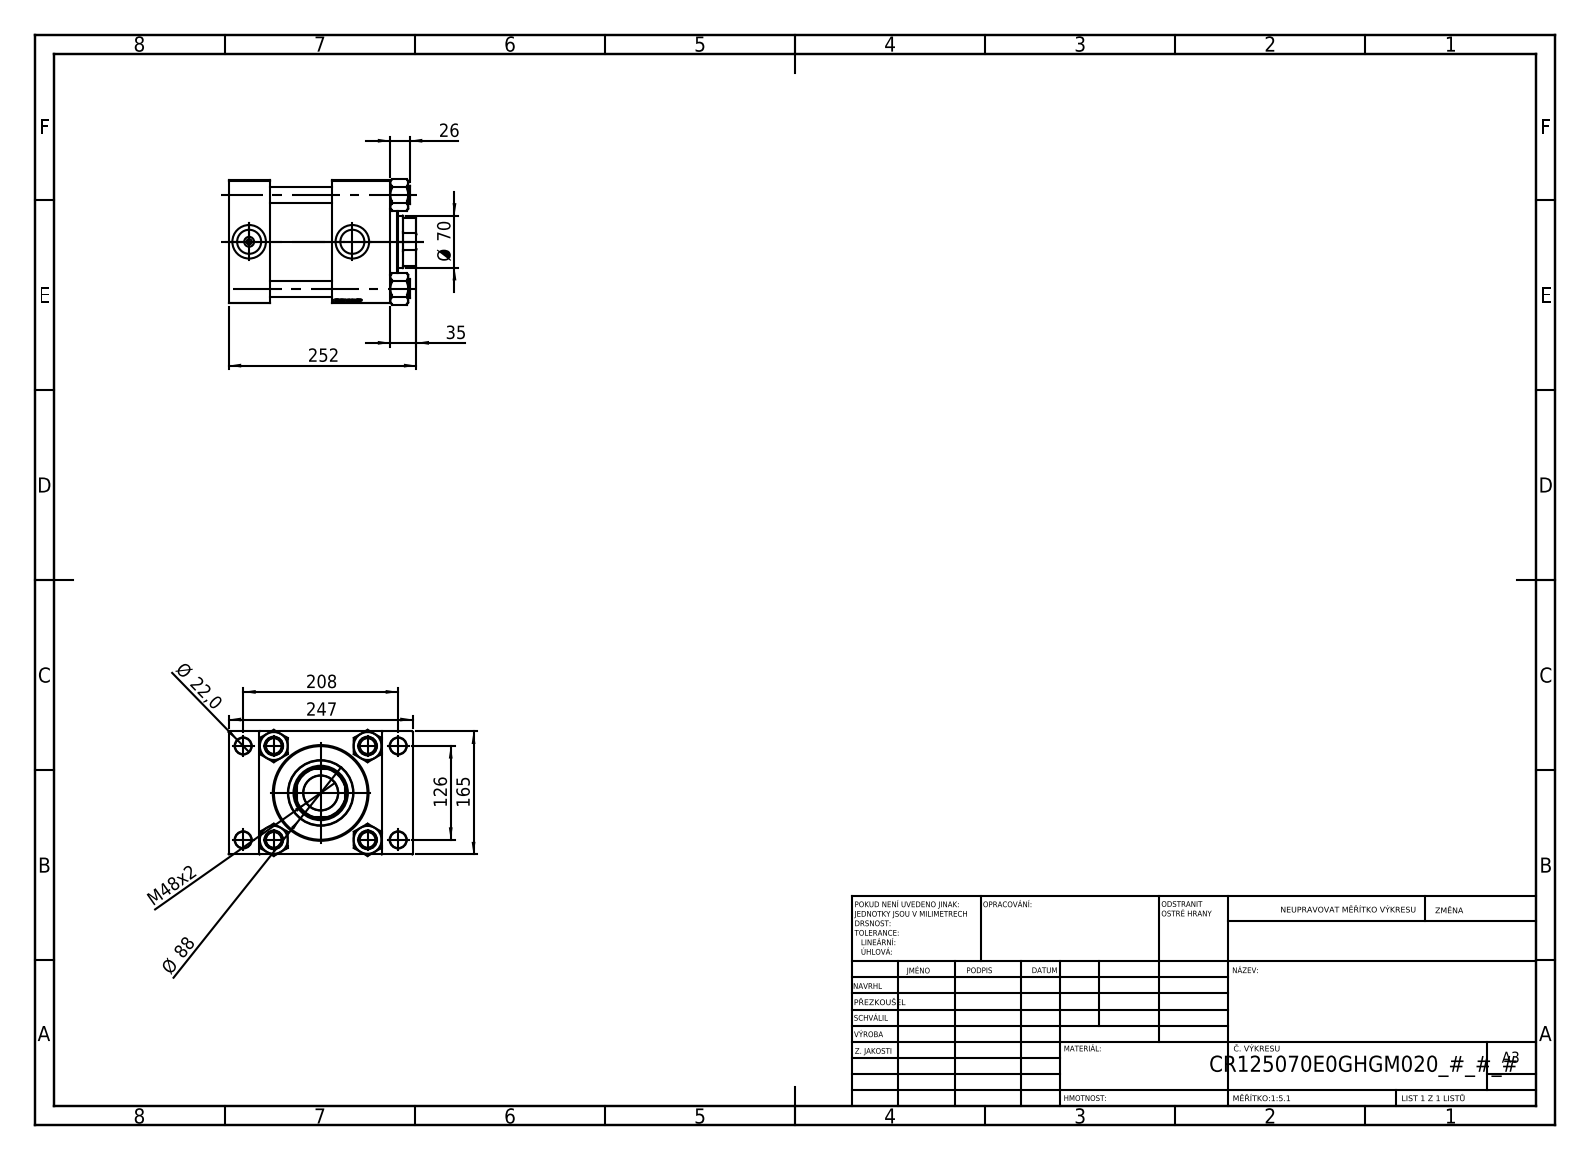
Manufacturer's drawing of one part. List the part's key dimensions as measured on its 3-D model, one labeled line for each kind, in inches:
Part name (STEP PRODUCT): V215CR_VCP_E; V215_VC_A; NUT_M5_E; V215CR_E_Body (+1 more)
STEP written by: SolidWorks 2019 (CONFIG_CONTROL_DESIGN)
Units: inches
Bodies: 11 solids, 1184 faces (546 planar, 86 cylindrical, 552 other)
Overall size (bounding box): 9.921 × 9.724 × 6.659
Volume: 322.4 in³ · Surface area: 898.7 in²
Round holes (diameter × count): ⌀0.866 ×8, ⌀0.276 ×2, ⌀1.269 ×2, ⌀1.772 ×2, ⌀1.831 ×1, ⌀2.756 ×1, ⌀2.874 ×1, ⌀3.78 ×1, ⌀4.921 ×1, ⌀4.941 ×1
Round bosses / shafts (diameter × count): ⌀0.984 ×4, ⌀5.157 ×1, ⌀3.465 ×1
Partial cylindrical surfaces — rounded edges, fillets, slot ends (radius × count): R1.339 ×1
Main face-to-face distances: 6.496, 2.165, 6.378, 8.543, 1.614, 5.472, 3.307, 3.071, 8.11, 7.413
Hole centre spacings: 1.616, 3.505, 4.787, 4.957, 5.215, 6.573, 8.233, 4.961
